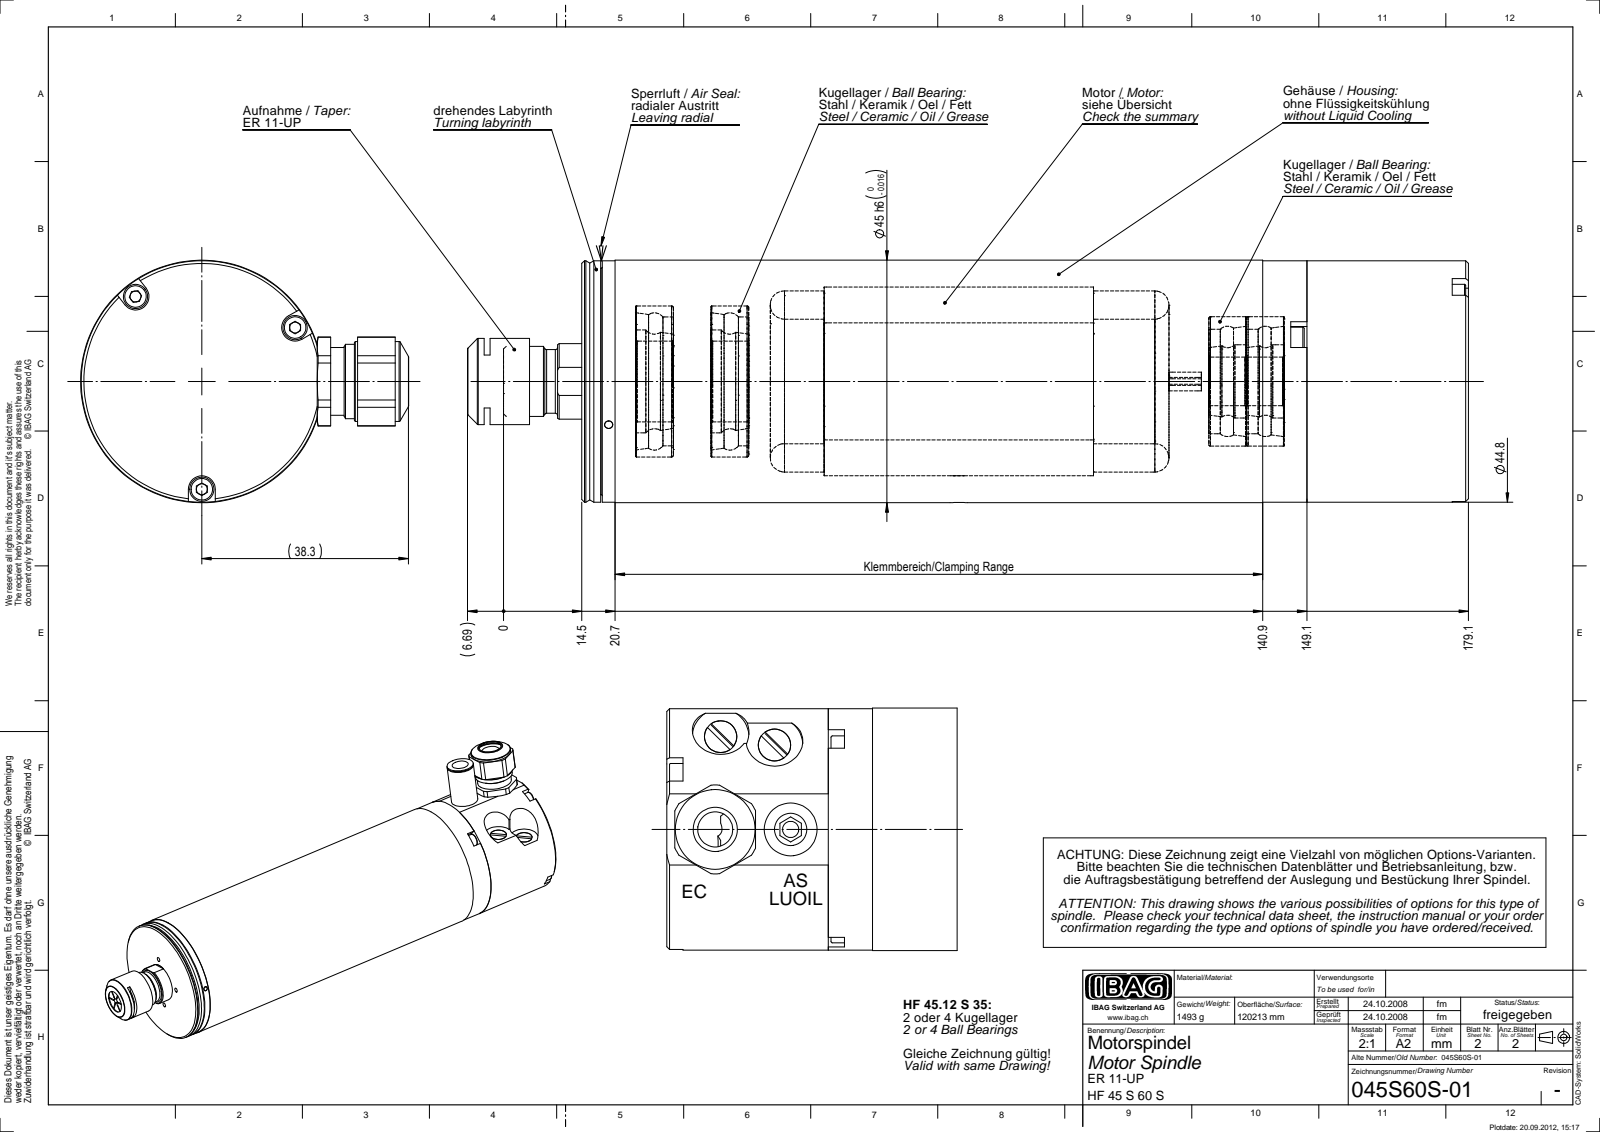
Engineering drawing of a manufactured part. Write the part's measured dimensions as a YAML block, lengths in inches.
part_name: "045S60S-01"
step_written_by: "SolidWorks 2012 (CONFIG_CONTROL_DESIGN)"
units: inches
bodies: {solids: 0, faces: 286, planar: 131, cylindrical: 98, other: 57}
overall_size: [7.315, 2.398, 1.772]
round_holes:
  - {diameter: 0.063, count: 4}
  - {diameter: 0.236, count: 3}
  - {diameter: 0.079, count: 1}
  - {diameter: 0.13, count: 1}
  - {diameter: 0.256, count: 1}
  - {diameter: 0.323, count: 1}
  - {diameter: 0.413, count: 1}
round_bosses_or_shafts:
  - {diameter: 0.177, count: 6}
  - {diameter: 1.772, count: 1}
  - {diameter: 1.764, count: 1}
  - {diameter: 0.63, count: 1}
  - {diameter: 0.583, count: 1}
  - {diameter: 0.551, count: 1}
  - {diameter: 0.543, count: 1}
  - {diameter: 0.512, count: 1}
partial_cylinders:
  - {radius: 0.098, count: 3}
  - {radius: 0.102, count: 3}
  - {radius: 0.059, count: 1}
  - {radius: 0.063, count: 1}
  - {radius: 0.207, count: 1}
  - {radius: 0.325, count: 1}
face_to_face_distances: [1.181, 5.299, 6.48, 0.244, 5.055, 6.236, 4.976, 4.732, 0.323, 1.504]
hole_center_spacings: [0.374, 0.529, 0.748, 0.551]
